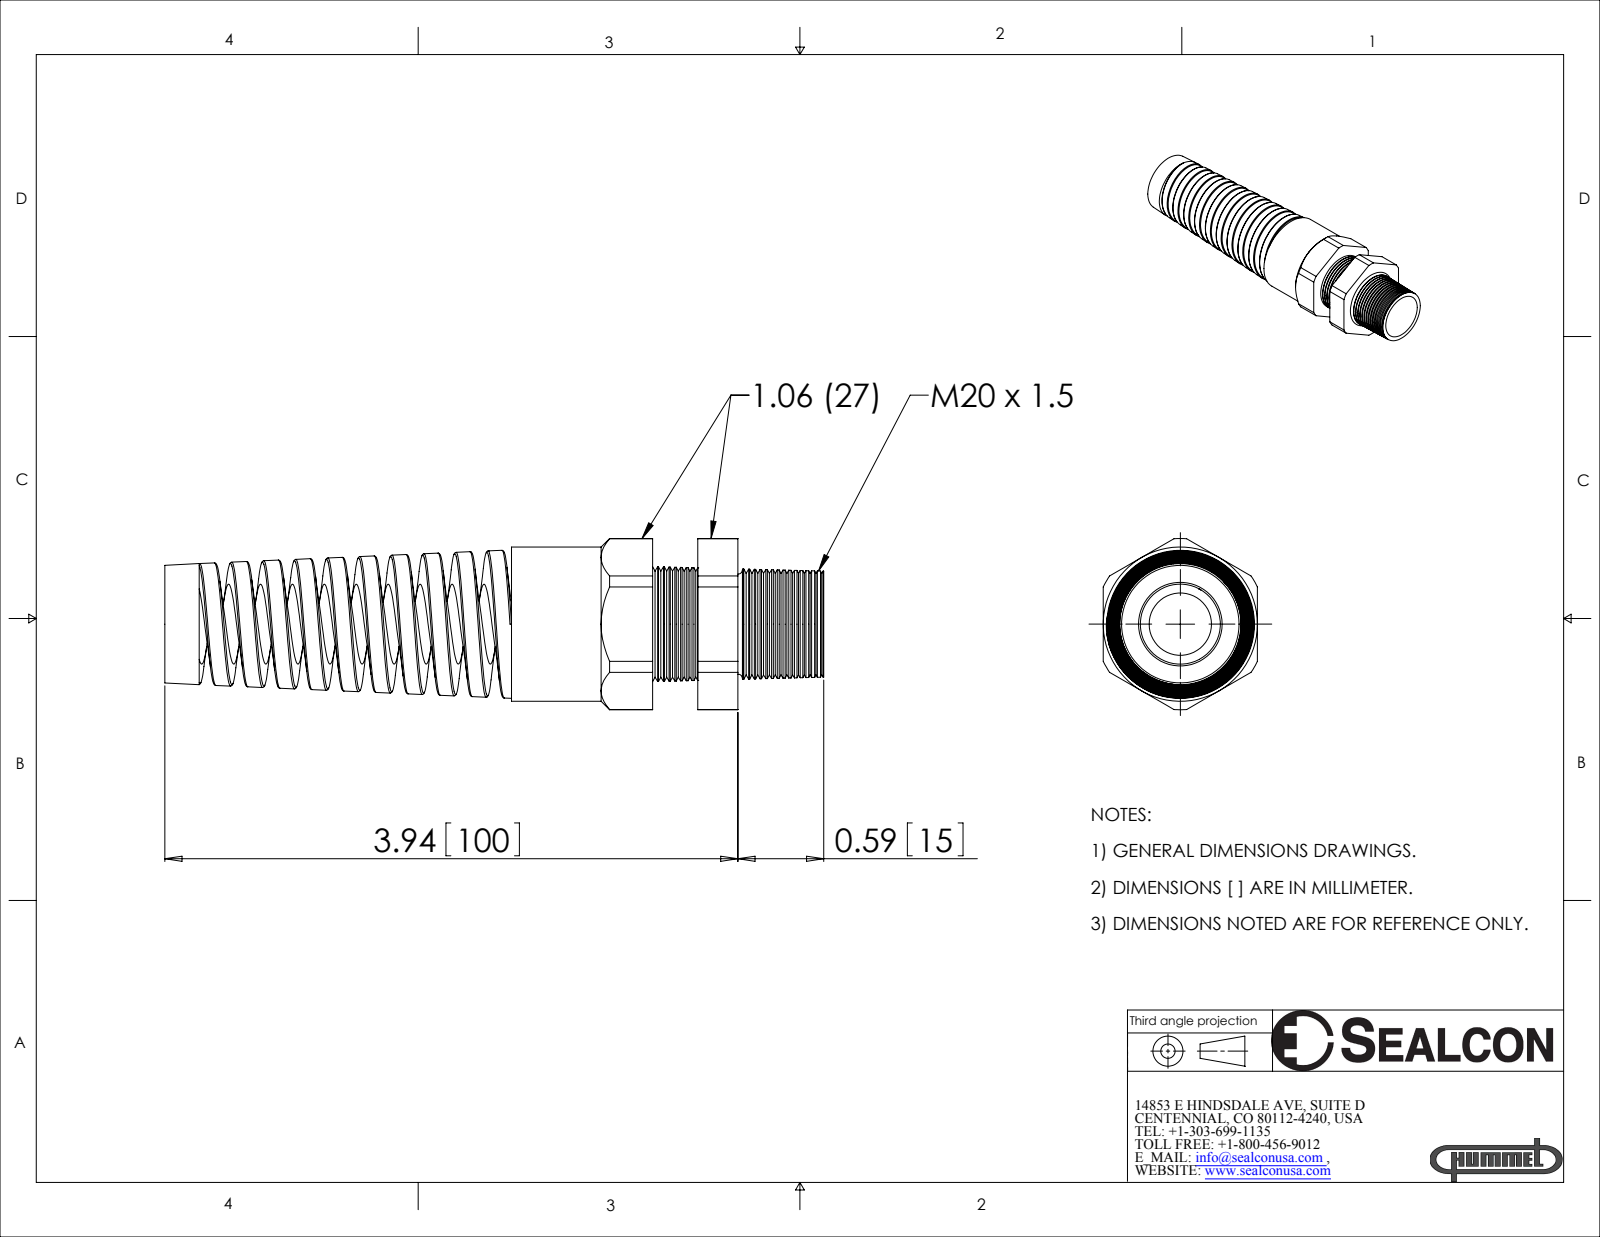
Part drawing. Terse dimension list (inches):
name: CF22DR-BK
written by: SolidWorks 2008 (CONFIG_CONTROL_DESIGN)
unit: in
bodies: 2 solids, 254 faces (26 planar, 45 cylindrical, 183 other)
size: 4.53 × 1.177 × 1.06
volume: 1.655 in³; area: 30.67 in²
holes: 1× ⌀0.428, 1× ⌀0.55, 1× ⌀0.575
bosses: 1× ⌀1.06, 1× ⌀0.774
rounds: 1× R0.588
face distances: 1.06, 0.311, 0.586, 0.276, 0.354, 0.665, 0.941, 0.616, 0.97, 1.281
